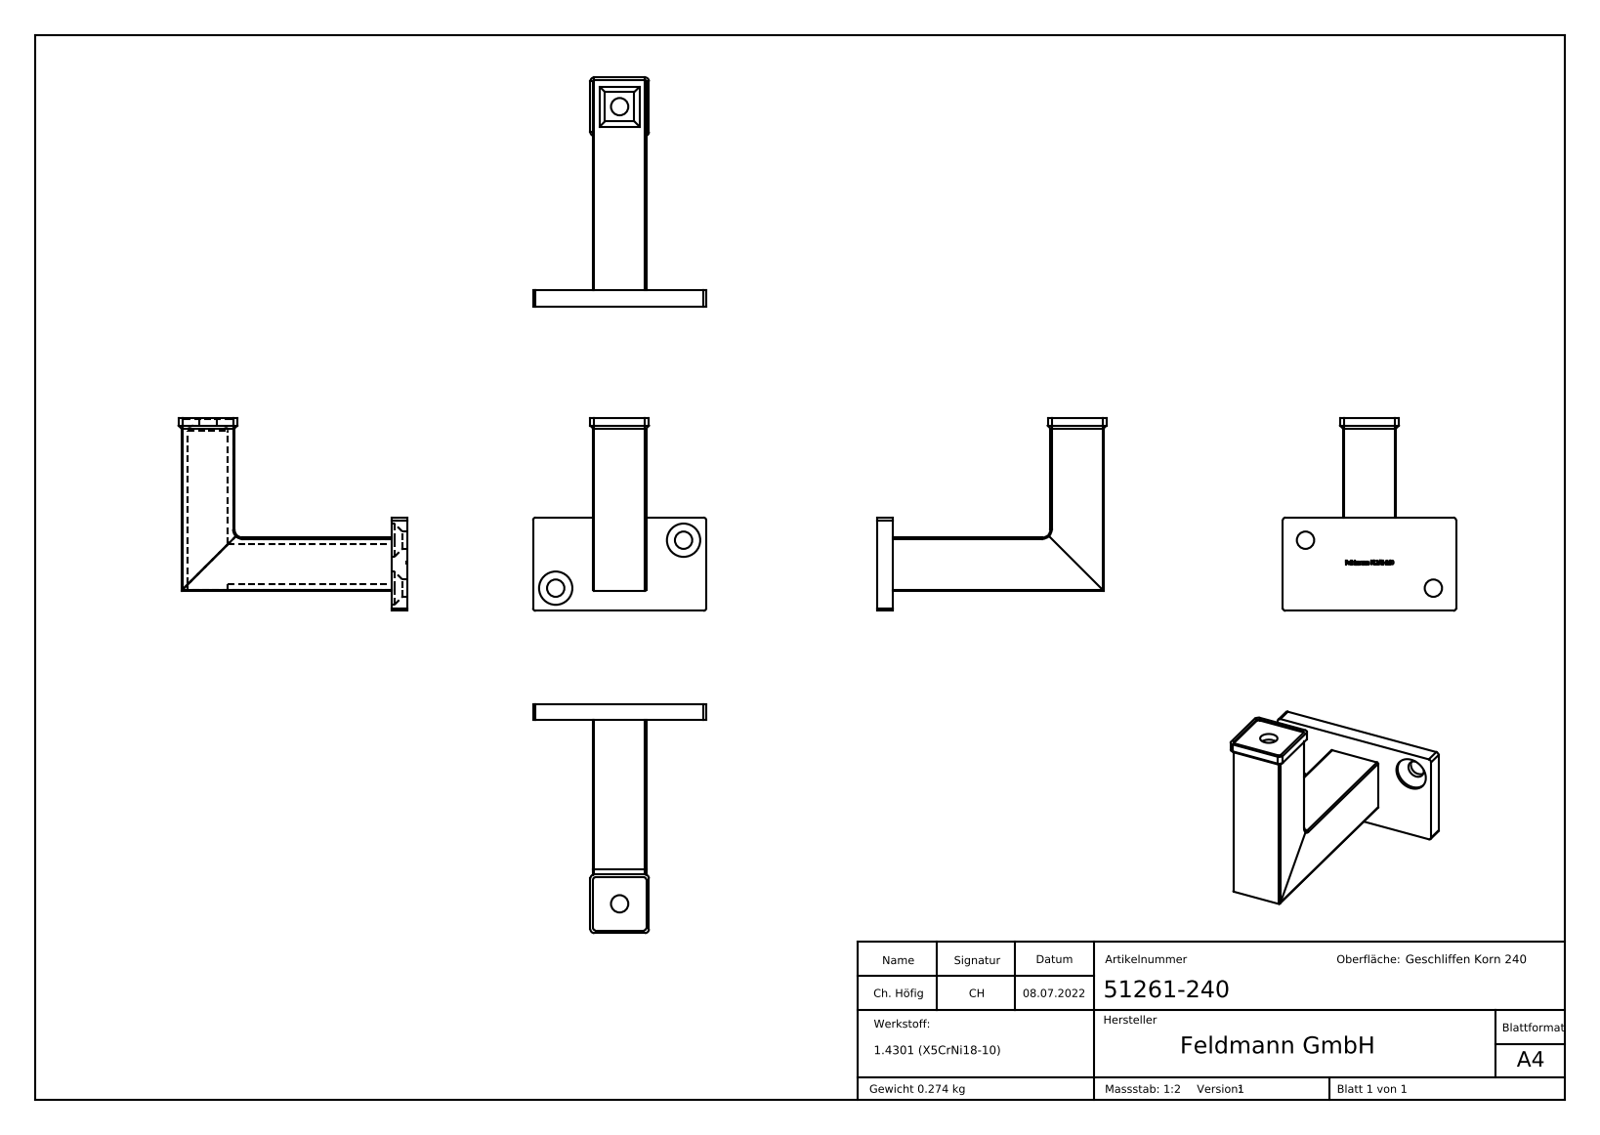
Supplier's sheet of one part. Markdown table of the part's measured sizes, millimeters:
| quantity | value |
| --- | --- |
| part name | 51261-240 |
| STEP written by | SolidWorks 2018 (CONFIG_CONTROL_DESIGN) |
| units | millimeters |
| bodies | 1 solid, 292 faces (166 planar, 30 cylindrical, 96 other) |
| overall size | 86 × 72.5 × 65 |
| volume | 34 703 mm³ |
| surface area | 23 196 mm² |
| round holes (diameter × count) | 6.5 × 3, 12.5 × 2 |
| partial cylindrical surfaces (radius × count) | 0.5 × 8, 1 × 8, 1.5 × 4, 2 × 4, 3 × 1 |
| main face-to-face distances | 2.5, 17.5, 20, 15, 6, 85, 79, 25, 65, 82.5 |
| hole center spacings | 51.26 |
